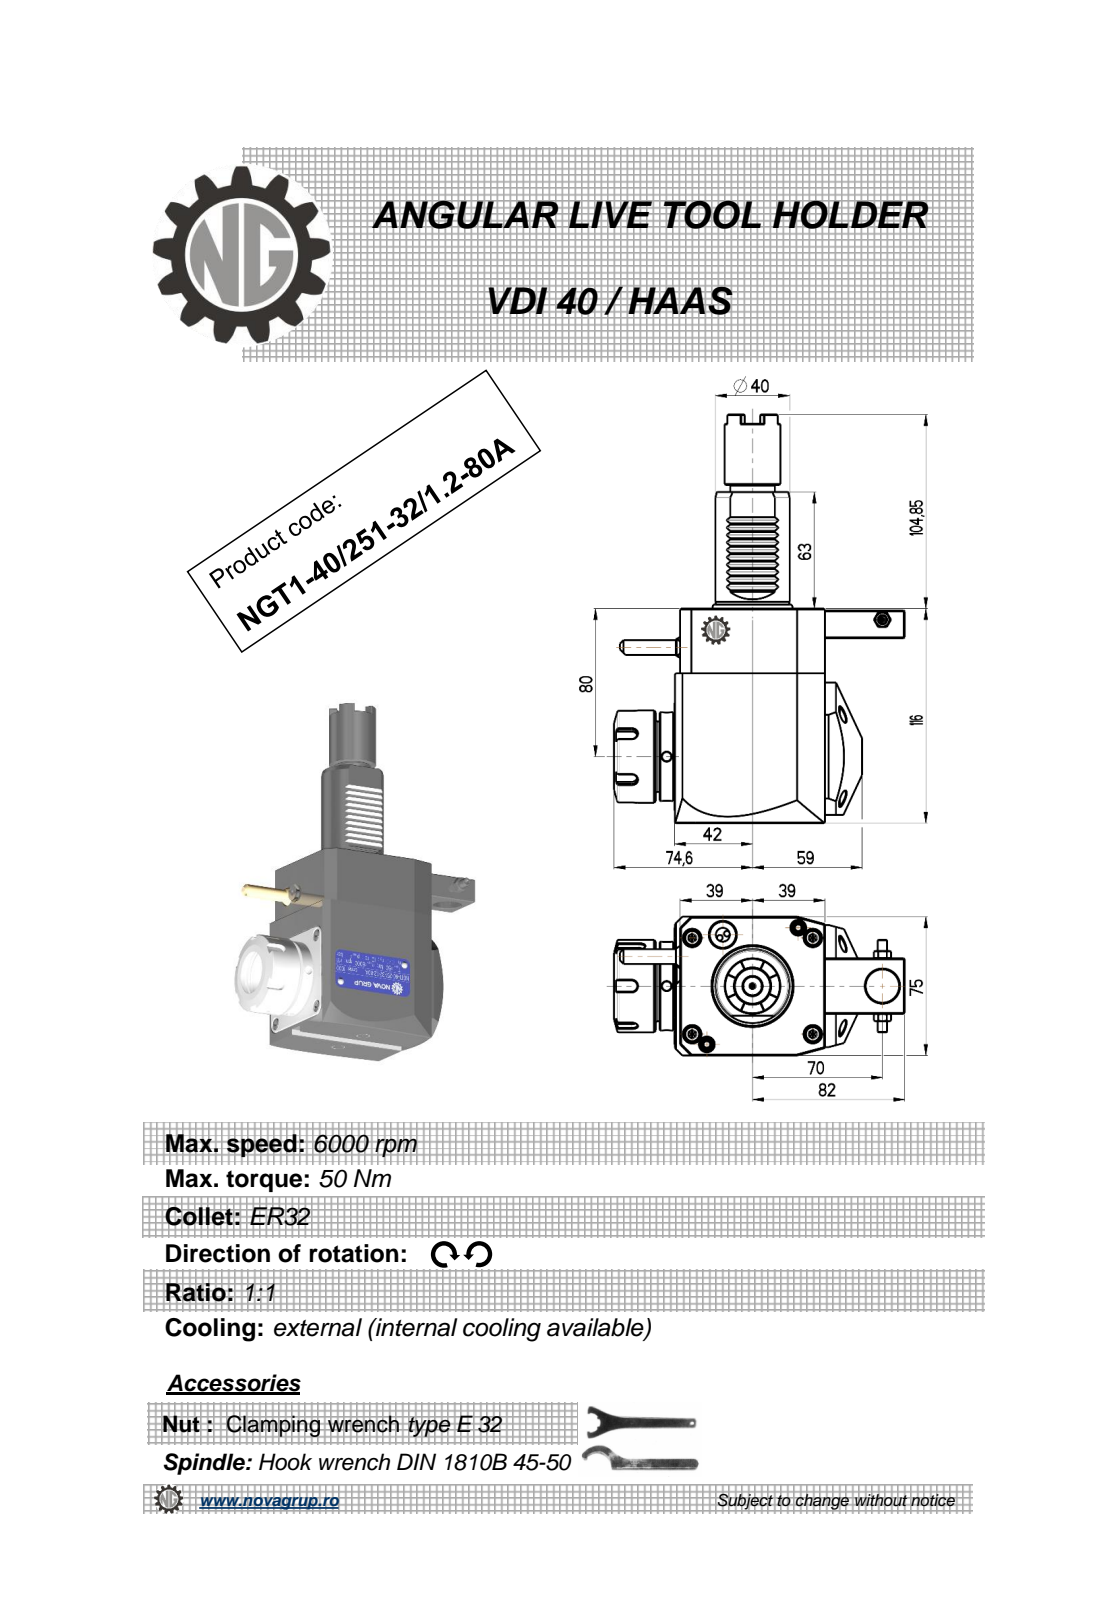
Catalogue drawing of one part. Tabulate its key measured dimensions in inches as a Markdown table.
| quantity | value |
| --- | --- |
| part name | NGT1_40_251_32_1_2_80A |
| STEP written by | PRO/ENGINEER BY PARAMETRIC TECHNOLOGY CORPORATION, 2010280 (CONFIG_CONTROL_DESIGN) |
| units | inches |
| bodies | 1 solid, 453 faces (222 planar, 94 cylindrical, 137 other) |
| overall size | 8.695 × 6.165 × 3.016 |
| volume | 55.51 in³ |
| surface area | 117.9 in² |
| round holes (diameter × count) | 0.197 × 3, 0.118 × 1, 0.165 × 1, 0.374 × 1, 0.709 × 1, 1.063 × 1 |
| round bosses / shafts (diameter × count) | 1.969 × 1, 1.89 × 1, 1.614 × 1, 1.575 × 1, 1.181 × 1, 0.791 × 1, 0.394 × 1, 0.353 × 1 |
| partial cylindrical surfaces (radius × count) | 0.01 × 12, 0.012 × 10, 0.008 × 6, 0.118 × 5, 0.02 × 1, 0.384 × 1, 1.575 × 1 |
| main face-to-face distances | 2.953, 4.567, 3.189, 0.118, 3.071, 0.11, 3.181, 0.039, 0.886, 2.067 |
| hole center spacings | 0.824, 2.407, 2.854, 4.577, 5.425 |
